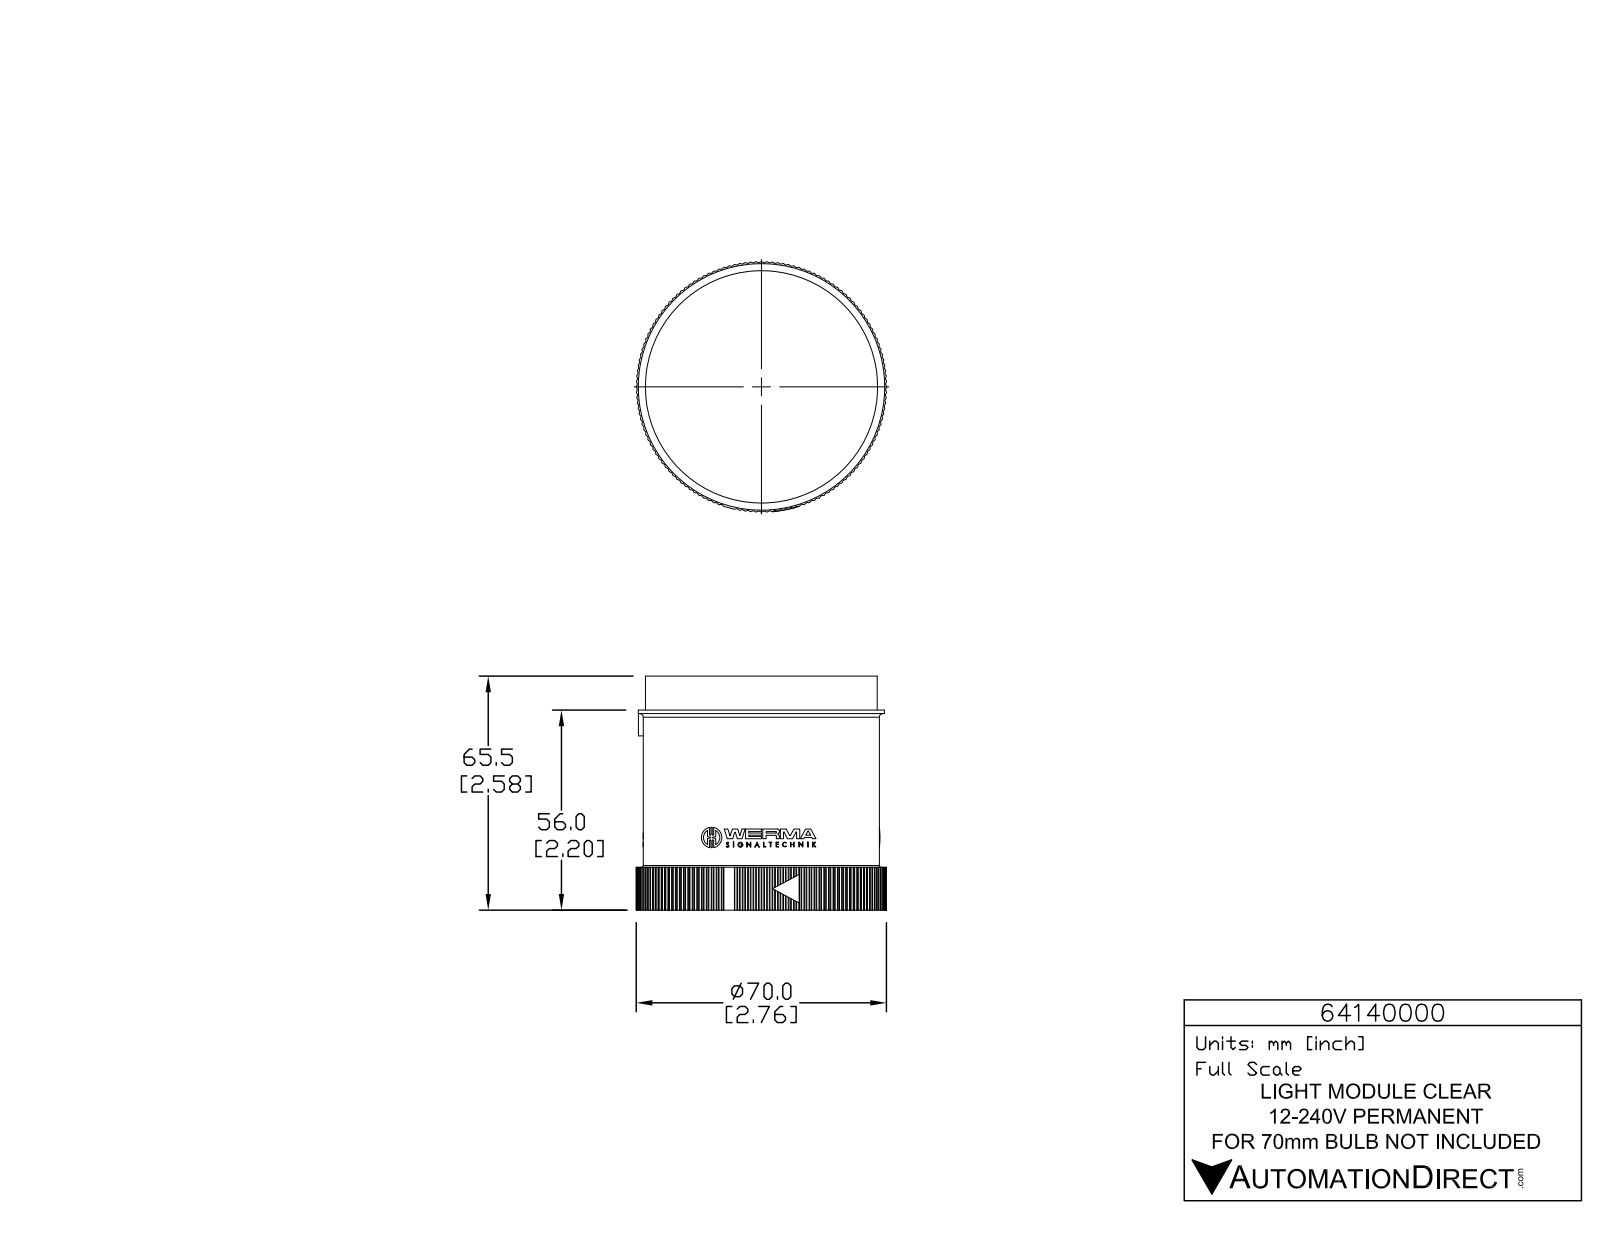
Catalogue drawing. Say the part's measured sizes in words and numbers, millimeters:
The part is named "64140000". Its 3-D file was written by "SolidWorks 2015 (AUTOMOTIVE_DESIGN)". It is 1 solid with 1400 faces: 832 planar, 563 cylindrical and 5 other. Overall it measures 70.2 by 70.2 by 65.5 millimeters. Its volume is 197 000 cubic millimeters and its surface area 24 180 square millimeters. Round holes: 3 of diameter 1, 1 of diameter 65.4. Round bosses or shafts: 3 of diameter 5.7, 3 of diameter 1.4, 1 of diameter 69, 1 of diameter 66.2, 1 of diameter 65. Partial cylindrical surfaces (rounded edges, fillets, slot ends): 285 of radius 0.2, 6 of radius 0.2, 6 of radius 0.2, 6 of radius 0.2, 6 of radius 3.3, 3 of radius 0.1, 3 of radius 0.1, 3 of radius 0.2. The main face-to-face distances are 55.9, 62.3, 9.6, 65.5, 56, 46.4, 9.5, 62.3, 12, 2.4.
